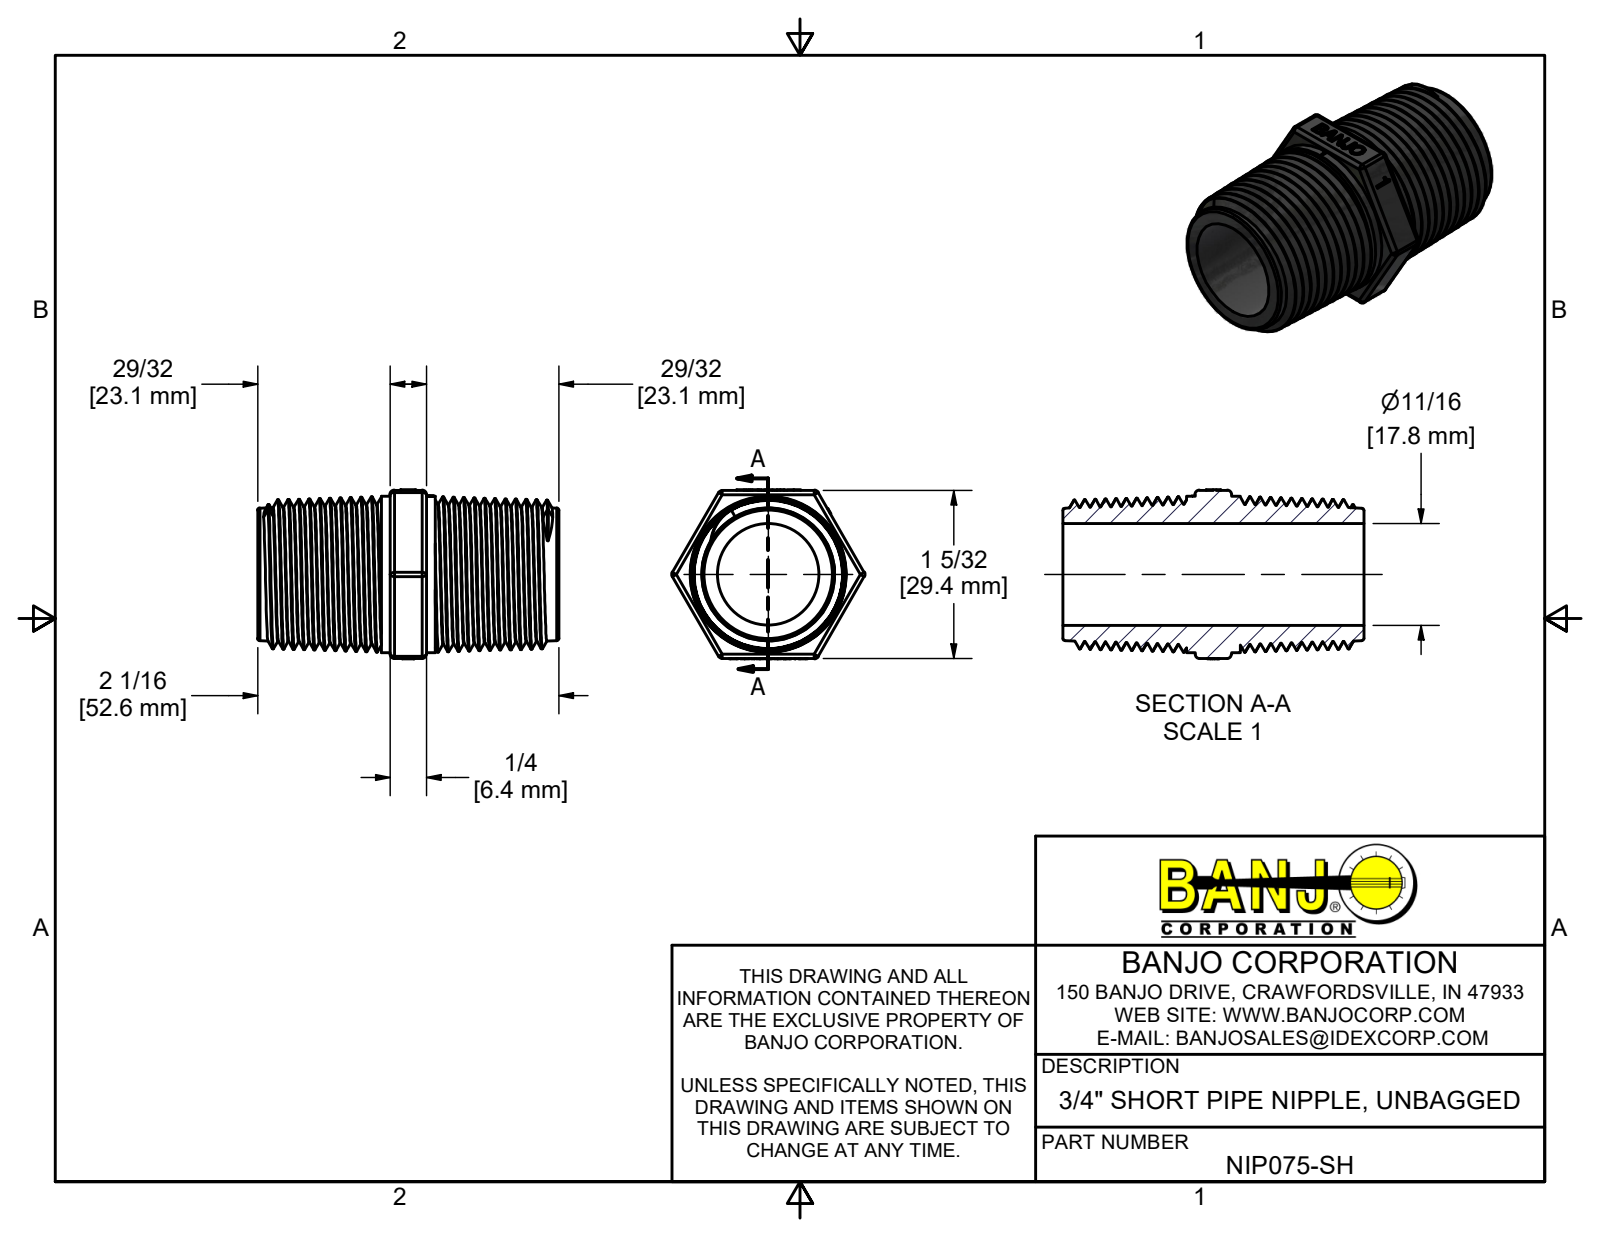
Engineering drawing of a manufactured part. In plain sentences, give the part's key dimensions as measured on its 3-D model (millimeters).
The part is named "NIP075-SH". Its 3-D file was written by "Autodesk Inventor 2014 (AUTOMOTIVE_DESIGN)". It is 1 solid with 89 faces: 21 planar, 21 cylindrical and 47 other. Overall it measures 45.72 by 33.2 by 28.96 millimeters. Its volume is 12 016 cubic millimeters and its surface area 9 181 square millimeters. Round holes: 1 of diameter 17.78. Partial cylindrical surfaces (rounded edges, fillets, slot ends): 18 of radius 0.76, 1 of radius 7.09. The main face-to-face distances are 20.32, 25.4, 28.96, 5.08, 45.72, 29.47, 0.51, 23.12, 2.8, 2.28.
